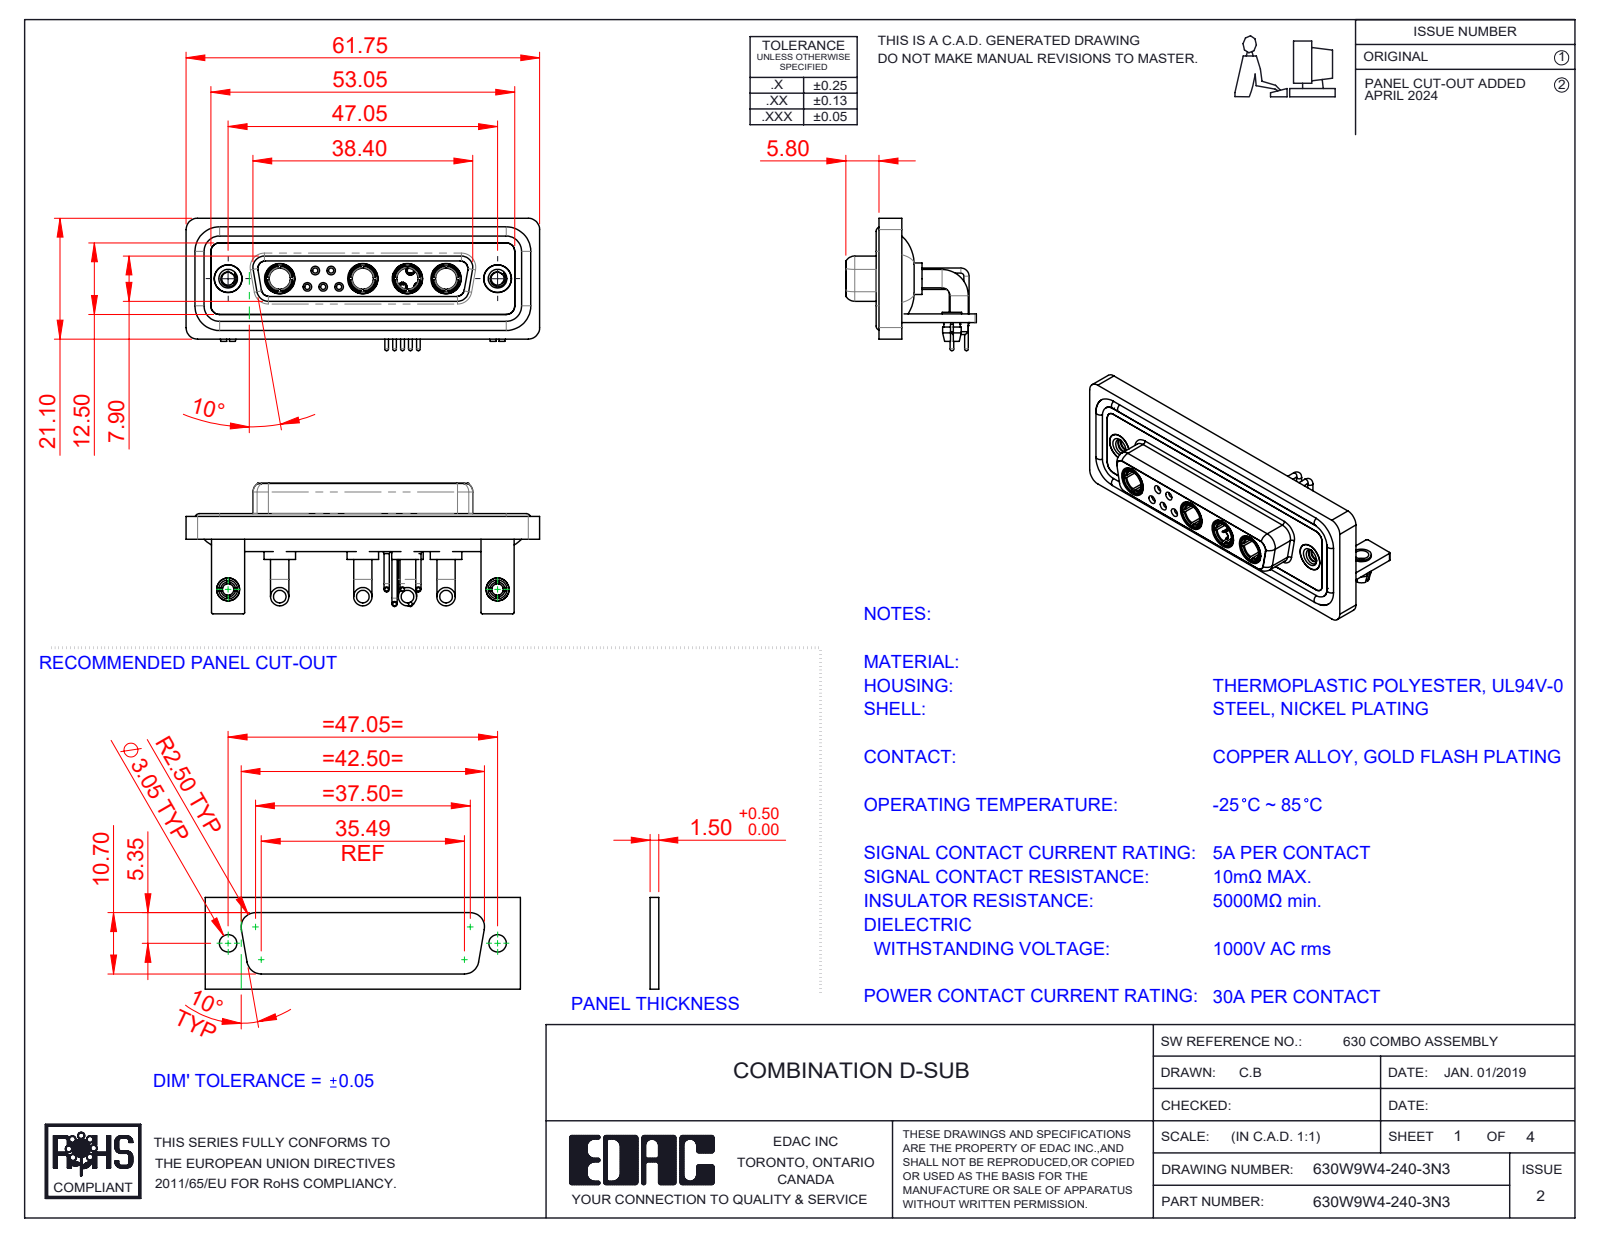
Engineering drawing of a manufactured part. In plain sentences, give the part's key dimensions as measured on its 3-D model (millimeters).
The part is named "630Combo Waterproof Housing_25 Contacts; 630Combo Shell Rear_25 Contacts; 630Combo Stabilizer Bracket_50 Contacts; 630Combo Shell Front_25 Contacts (+7 more)". Its 3-D file was written by "SolidWorks 2023 (CONFIG_CONTROL_DESIGN)". It is 24 solids with 1103 faces: 364 planar, 459 cylindrical and 280 other. Overall it measures 61.75 by 23.12 by 22.8 millimeters. Its volume is 8 966 cubic millimeters and its surface area 15 066 square millimeters. Round holes: 7 of diameter 2, 6 of diameter 4.85, 5 of diameter 0.9, 5 of diameter 1.1, 5 of diameter 1.5, 4 of diameter 3.7, 4 of diameter 5.3, 3 of diameter 1.6, 2 of diameter 1.7, 2 of diameter 2.26, 2 of diameter 2.5, 2 of diameter 3.2. Round bosses or shafts: 10 of diameter 0.9, 9 of diameter 1.6, 8 of diameter 3.2, 5 of diameter 2, 5 of diameter 1.5, 5 of diameter 0.65, 4 of diameter 5.5, 4 of diameter 5.2. Partial cylindrical surfaces (rounded edges, fillets, slot ends): 19 of radius 2, 18 of radius 1.5, 16 of radius 0.25, 8 of radius 1.35, 8 of radius 1.6, 5 of radius 0.5, 4 of radius 0.6, 4 of radius 0.65. The main face-to-face distances are 0.4, 1.8, 2.9, 3.7, 1.5, 4.1, 1.1, 1.4, 1.6, 2.5. The hole center spacings are 3.16, 2.77, 5.04, 13.85, 11.08, 12.79, 15.5, 5.54.
